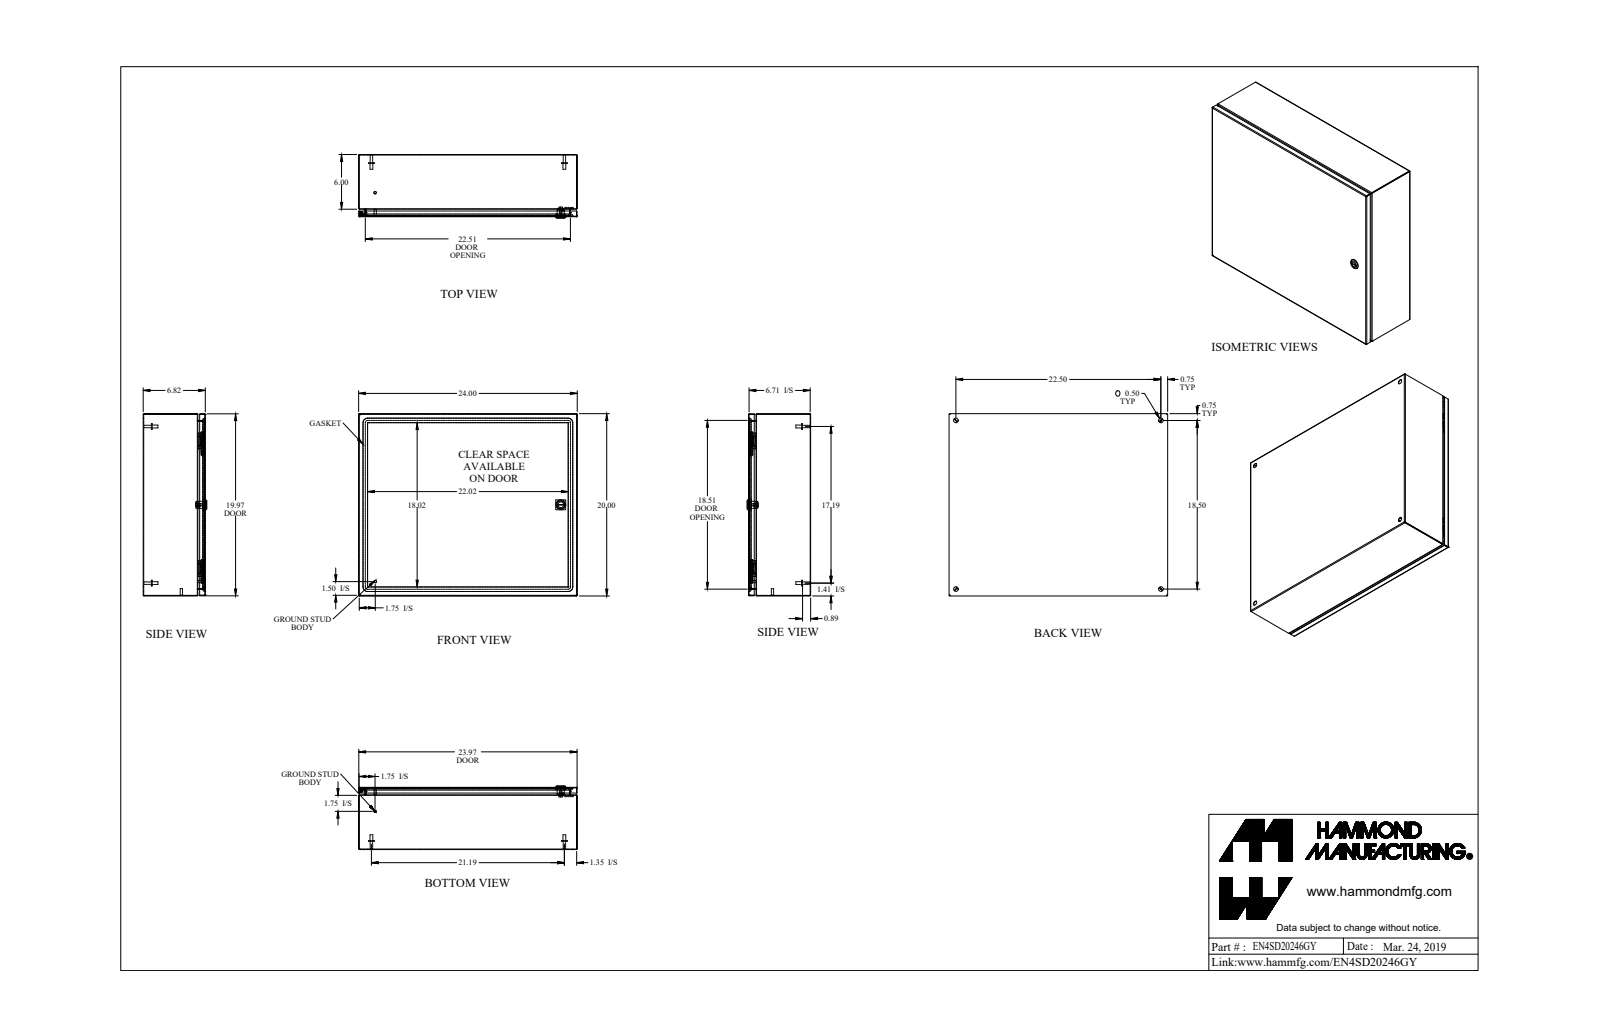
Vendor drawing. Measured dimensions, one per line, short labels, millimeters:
name: EN4SD20246GY_Default
written by: SolidWorks 2019 (CONFIG_CONTROL_DESIGN)
unit: mm
bodies: 21 solids, 634 faces (285 planar, 213 cylindrical, 136 other)
size: 609.6 × 508 × 177.3
volume: 1 691 000 mm³; area: 2 266 000 mm²
holes: 4× ⌀12.7, 1× ⌀4.4, 1× ⌀5.9, 1× ⌀6.1, 1× ⌀6.1, 1× ⌀15.9, 1× ⌀19.9
bosses: 4× ⌀15.9, 4× ⌀8, 4× ⌀6.9, 2× ⌀7.1, 2× ⌀6.4, 1× ⌀27.9, 1× ⌀13.3, 1× ⌀11.6
rounds: 21× R0.7, 21× R2.2, 16× R6.4, 8× R482.6, 4× R0.2, 4× R1.6, 4× R12.7, 2× R3.2
face distances: 1.4, 171.8, 170.4, 173.3, 506.6, 608.2, 505.1, 508, 606.7, 609.6
hole spacings: 469.9, 571.5, 593.1, 739.9, 236.5, 236.5
